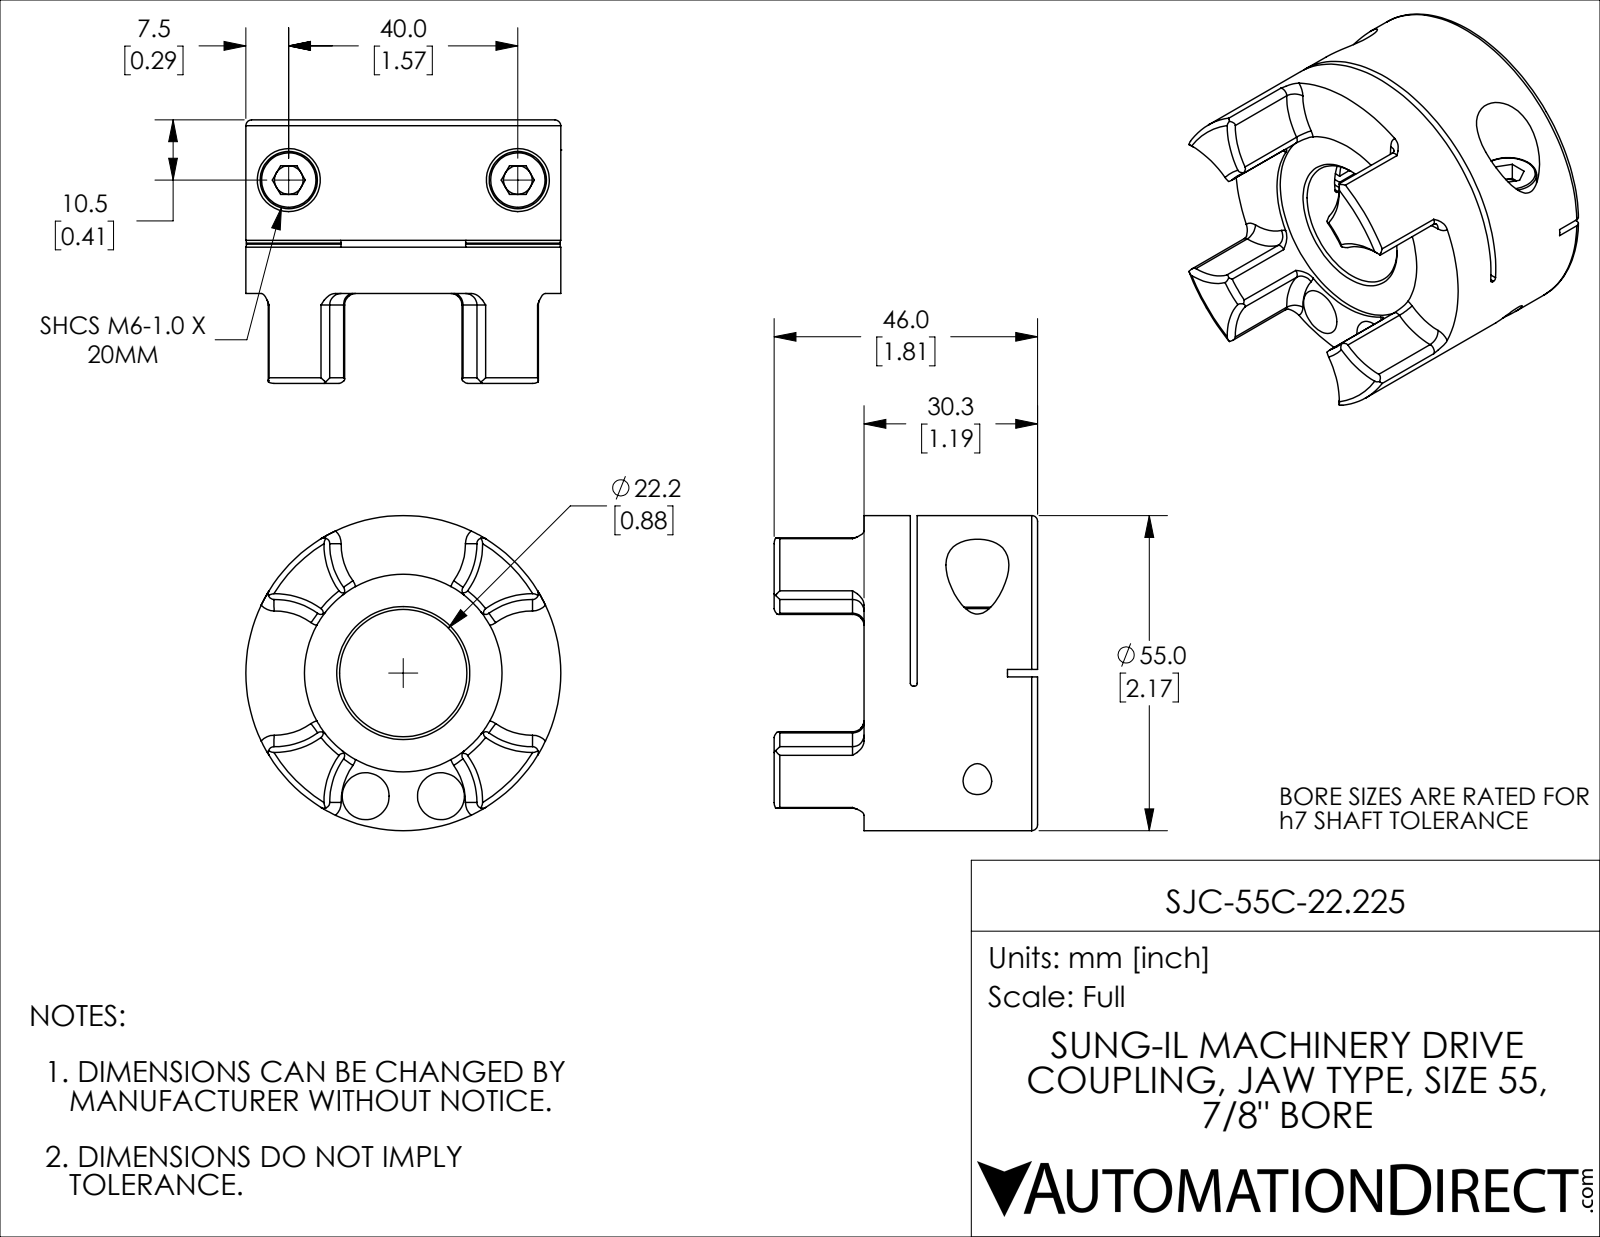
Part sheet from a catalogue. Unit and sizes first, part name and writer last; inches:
Units: inches
Overall size (bounding box): 2.165 × 2.165 × 1.811
Round holes (diameter × count): ⌀0.197 ×2, ⌀0.252 ×2, ⌀0.323 ×2, ⌀0.433 ×2, ⌀0.875 ×1, ⌀1.358 ×1
Round bosses / shafts (diameter × count): ⌀0.394 ×2, ⌀0.236 ×2, ⌀2.165 ×1
Partial cylindrical surfaces — rounded edges, fillets, slot ends (radius × count): R0.039 ×16, R0.506 ×4, R0.02 ×2, R1.969 ×1
Main face-to-face distances: 0.874, 0.047, 0.827, 0.319, 0.366, 1.193, 0.031, 0.287, 0.335, 1.161
Hole centre spacings: 0.885, 0.517, 1.575
Volume: 3.732 in³ · Surface area: 31.12 in²
Bodies: 3 solids, 212 faces (52 planar, 76 cylindrical, 84 other)
Part name (STEP PRODUCT): SJC-55C-22.225
STEP written by: SolidWorks 2021 (CONFIG_CONTROL_DESIGN)
